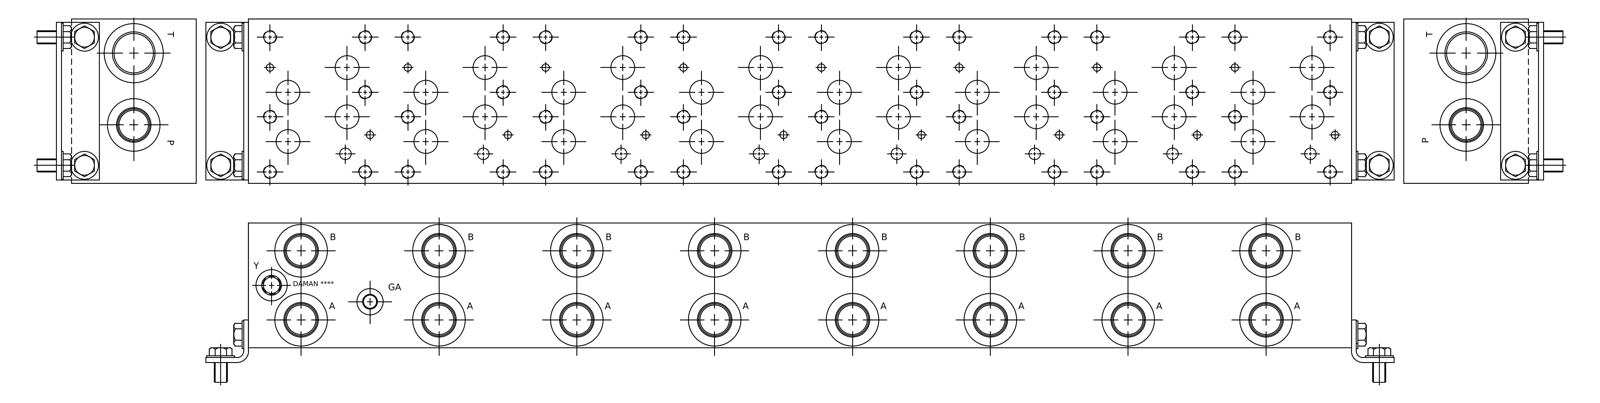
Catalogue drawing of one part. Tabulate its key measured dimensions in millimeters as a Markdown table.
| quantity | value |
| --- | --- |
| part name | C:\\\\Program Files (x86)\\\\PARO\\\\Hydroman 2010\\\\Export\\\\AD08P085S |
| STEP written by | Autodesk Inventor 2013 (AUTOMOTIVE_DESIGN) |
| units | millimeters |
| bodies | 1 solid, 2498 faces (1512 planar, 196 cylindrical, 790 other) |
| overall size | 1066.8 × 158.75 × 120.65 |
| volume | 19 540 000 mm³ |
| surface area | 792 649 mm² |
| round holes (diameter × count) | 10.72 × 51, 23.01 × 30, 31.27 × 17, 35.51 × 17, 48.97 × 17, 7.14 × 16, 28.57 × 8, 28.58 × 8, 11.13 × 7, 23.02 × 2, 11.11 × 1, 12.9 × 1 |
| main face-to-face distances | 120.65, 158.75, 0.79, 157.96, 1066.8, 4.06, 3.27, 1066.01, 154.69, 1065.22 |
| hole center spacings | 133.35, 266.7, 400.05, 533.4, 274.91, 666.75, 141.62, 149.09 |
